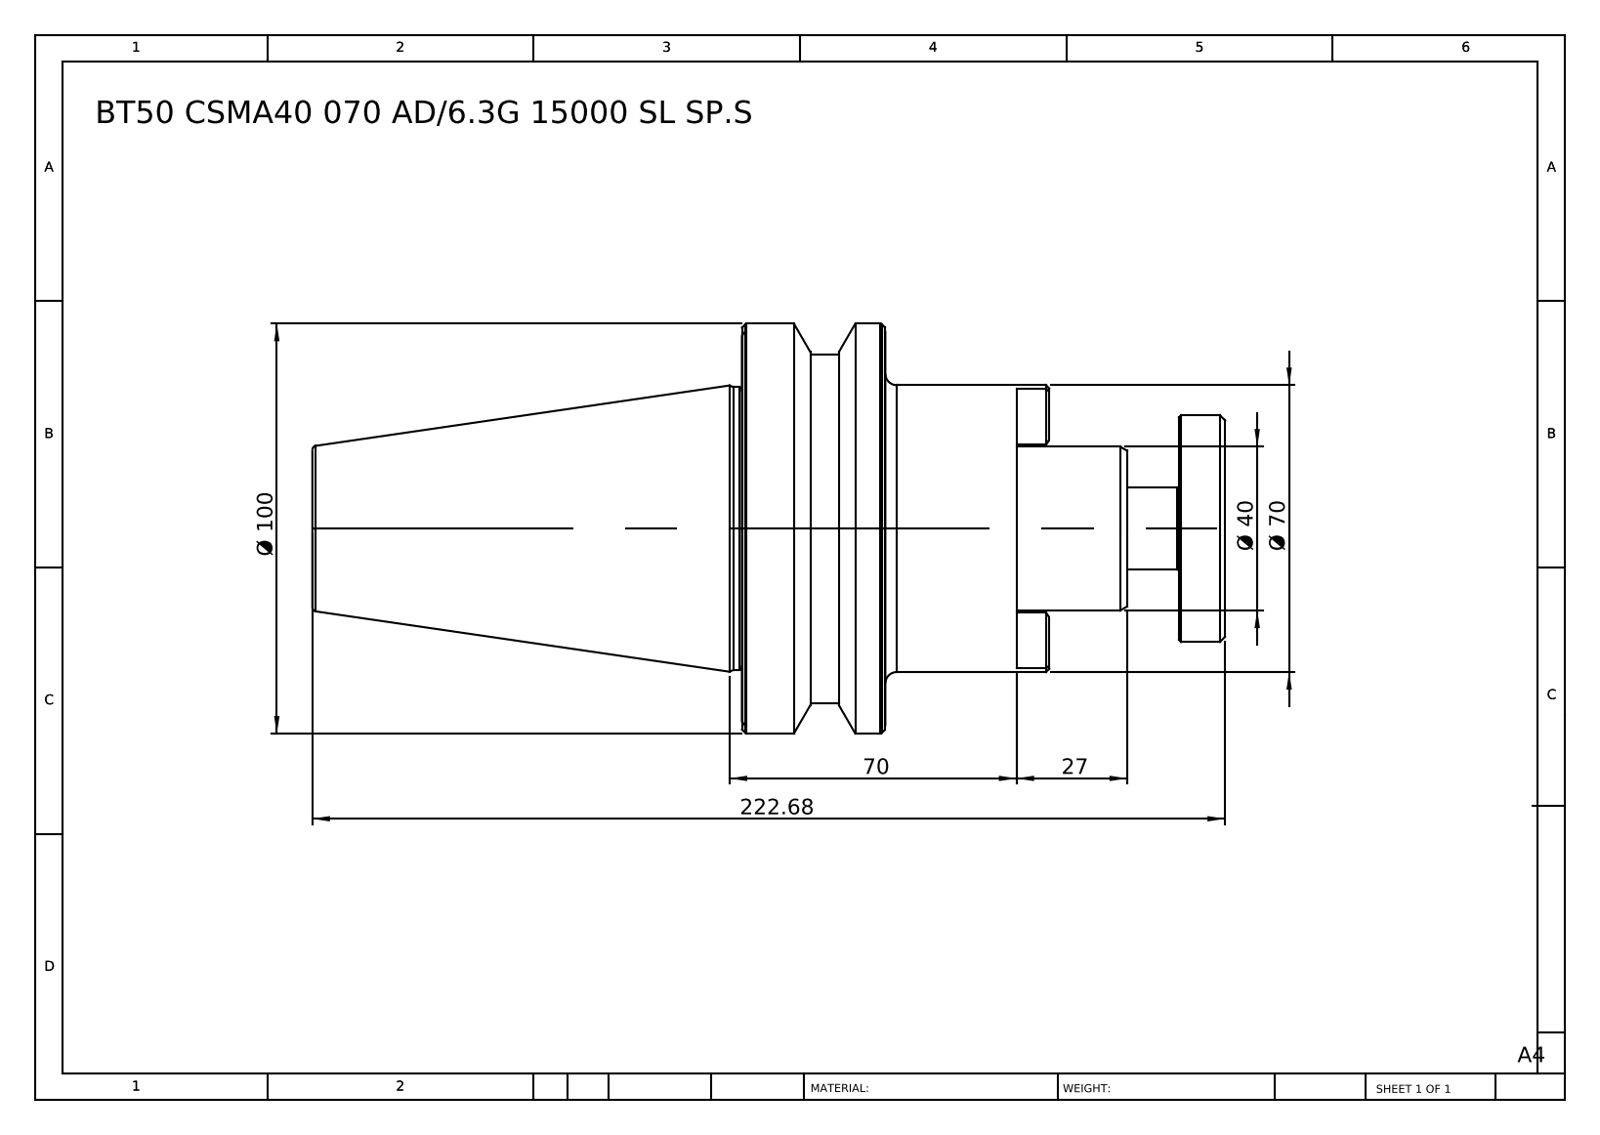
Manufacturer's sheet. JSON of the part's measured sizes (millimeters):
{"part_name": "BT50 CSMA40 070 AD-6.3G 15000 SL SP.S", "step_written_by": "SolidWorks 2014 (CONFIG_CONTROL_DESIGN)", "units": "millimeters", "bodies": {"solids": 1, "faces": 88, "planar": 20, "cylindrical": 19, "other": 49}, "overall_size": [222.68, 100, 100], "volume_mm3": 701597, "surface_area_mm2": 62094, "round_bosses_or_shafts": [[100, 1], [85, 1], [70, 1], [69, 1], [55.3, 1], [40, 1], [20, 1]], "partial_cylinders_radius": [[22, 1]], "face_to_face_distances": [35, 82.88, 117.88, 50.88, 32, 67, 11.23, 39.65, 71.65, 106.65]}
